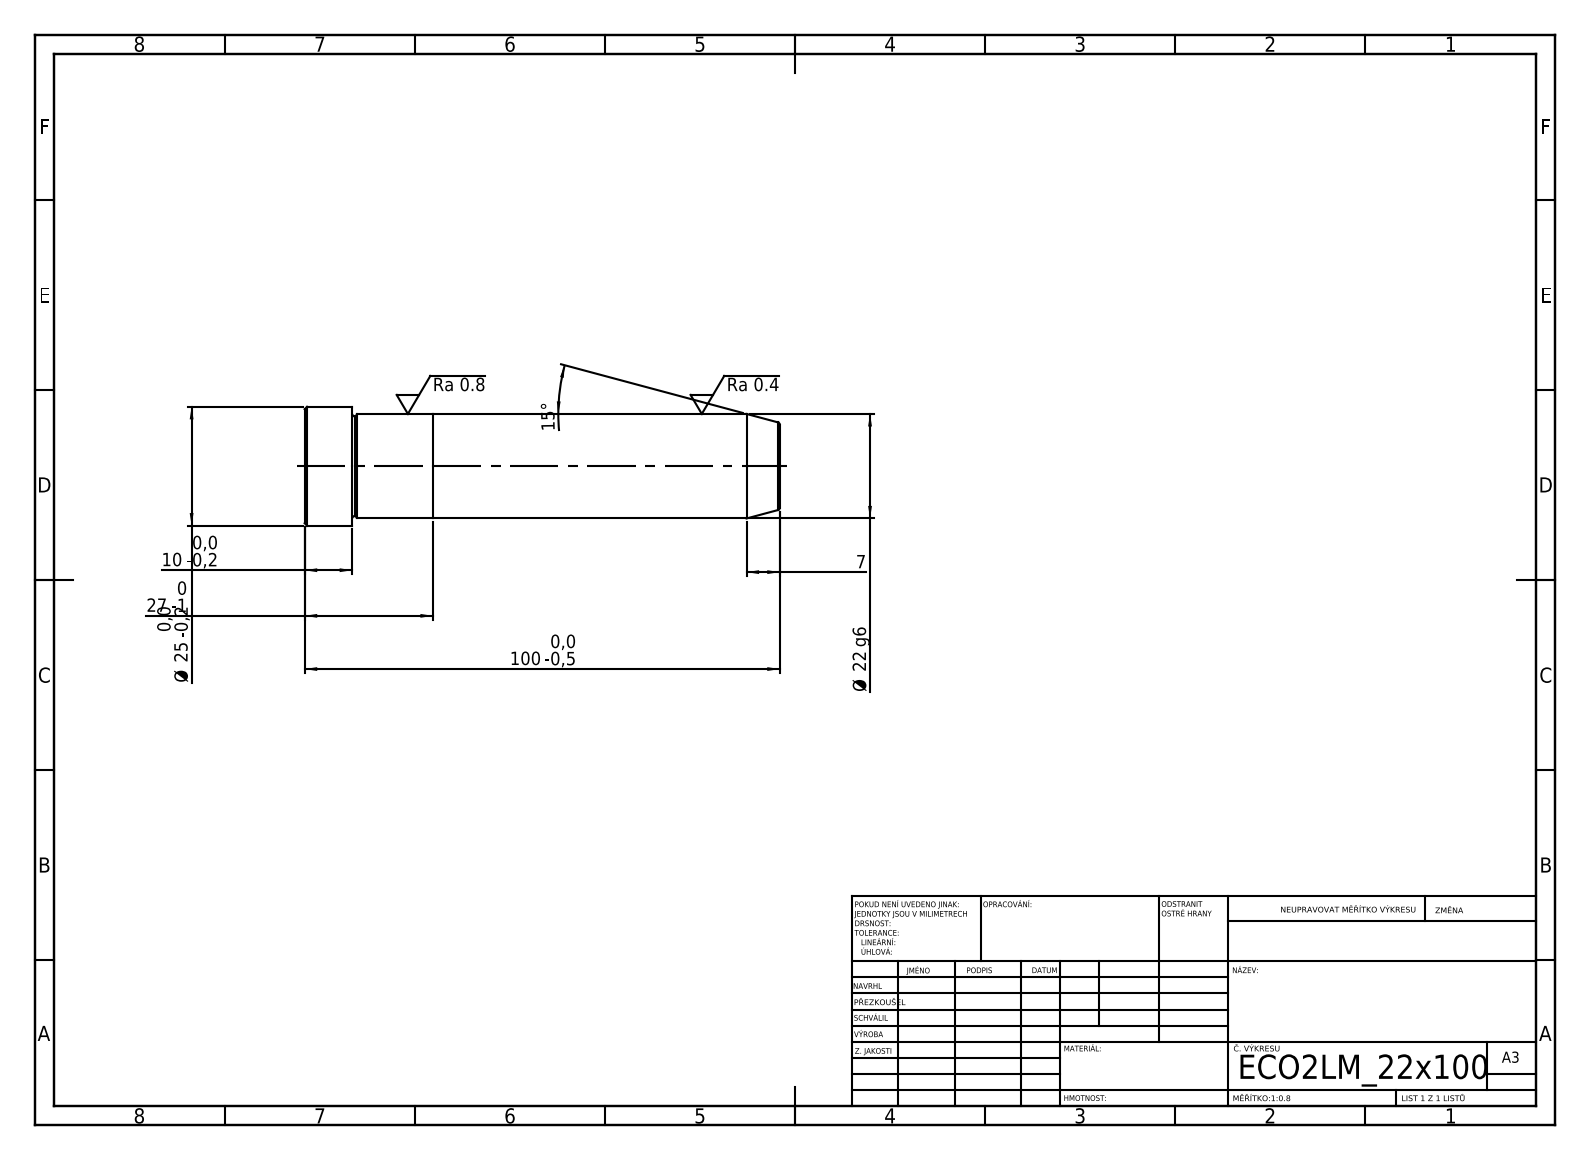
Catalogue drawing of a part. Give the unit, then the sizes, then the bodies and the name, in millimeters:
Units: millimetres
Overall size (bounding box): 100 × 25 × 25
Round bosses / shafts (diameter × count): ⌀25 ×1, ⌀22 ×1
Main face-to-face distances: 27, 73, 100, 90, 17, 10
Volume: 38 655 mm³ · Surface area: 8 610 mm²
Bodies: 2 solids, 21 faces (5 planar, 6 cylindrical, 10 other)
STEP written by: SolidWorks 2019 (CONFIG_CONTROL_DESIGN)
